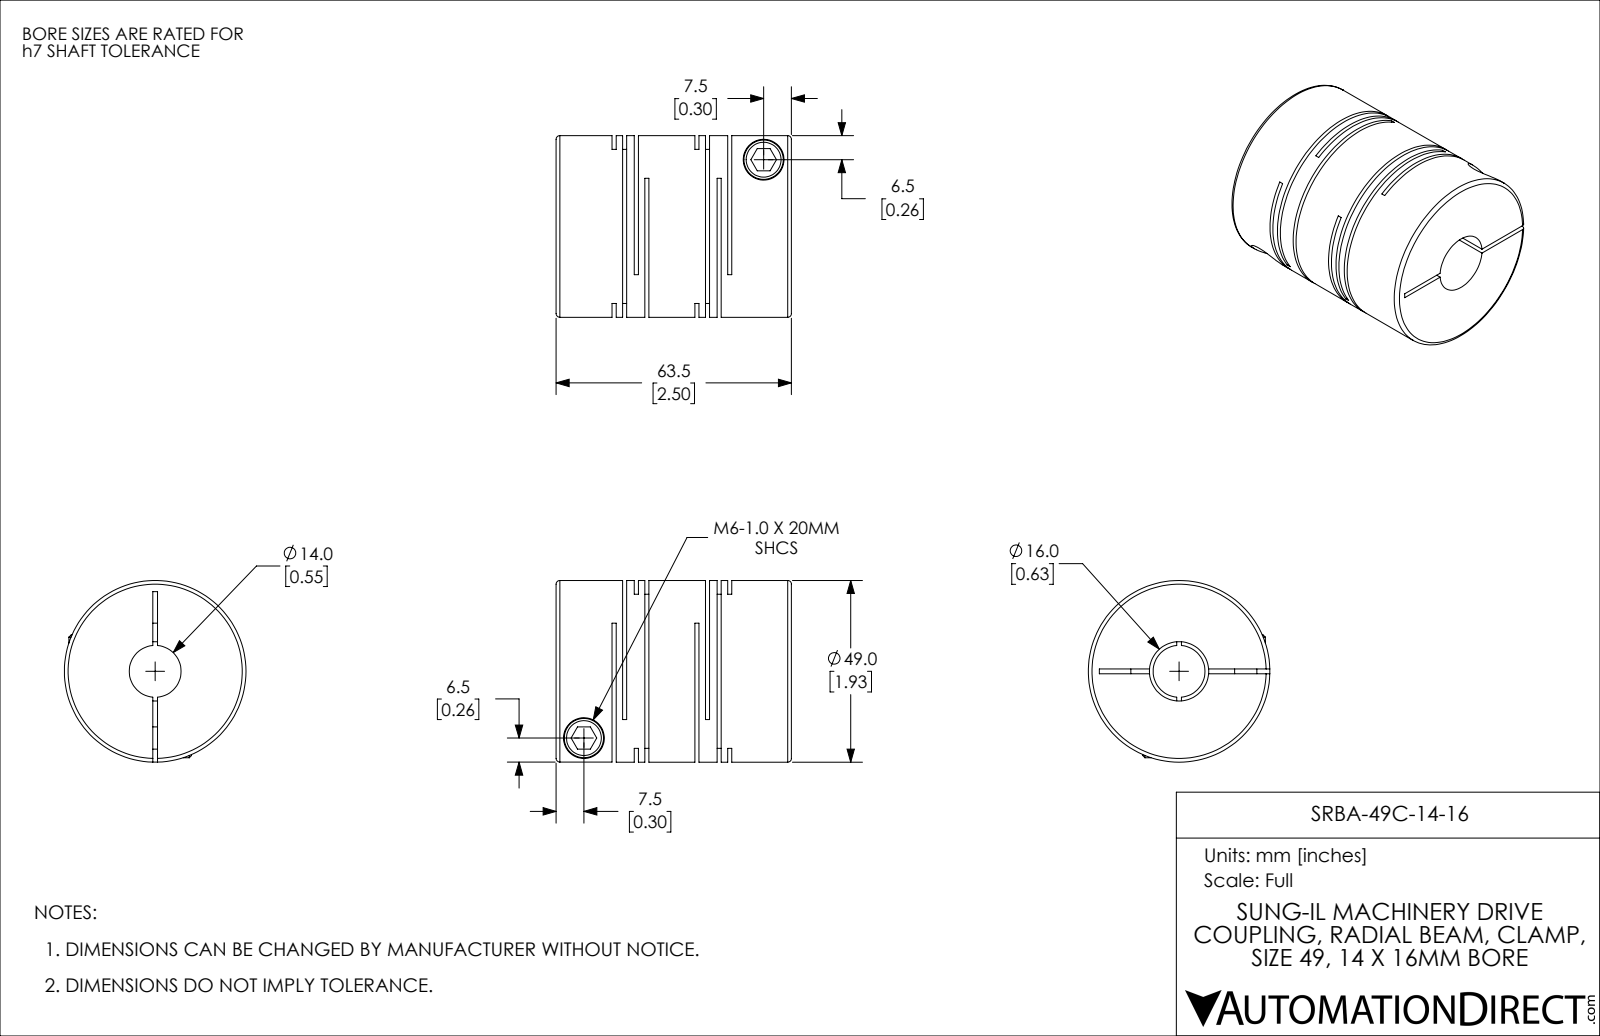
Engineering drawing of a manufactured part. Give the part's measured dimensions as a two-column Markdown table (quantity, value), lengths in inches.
| quantity | value |
| --- | --- |
| part name | SRBA-49C-14-16 |
| STEP written by | SolidWorks 2021 (CONFIG_CONTROL_DESIGN) |
| units | inches |
| bodies | 1 solid, 114 faces (60 planar, 42 cylindrical, 12 other) |
| overall size | 2.5 × 1.929 × 1.929 |
| volume | 5.671 in³ |
| surface area | 61.38 in² |
| round holes (diameter × count) | 0.236 × 2, 0.433 × 2, 0.551 × 1, 0.63 × 1 |
| round bosses / shafts (diameter × count) | 0.417 × 2, 1.929 × 1 |
| main face-to-face distances | 0.236, 0.043, 0.112, 0.88, 0.069, 0.193, 0.837, 0.124, 0.768, 0.644 |
